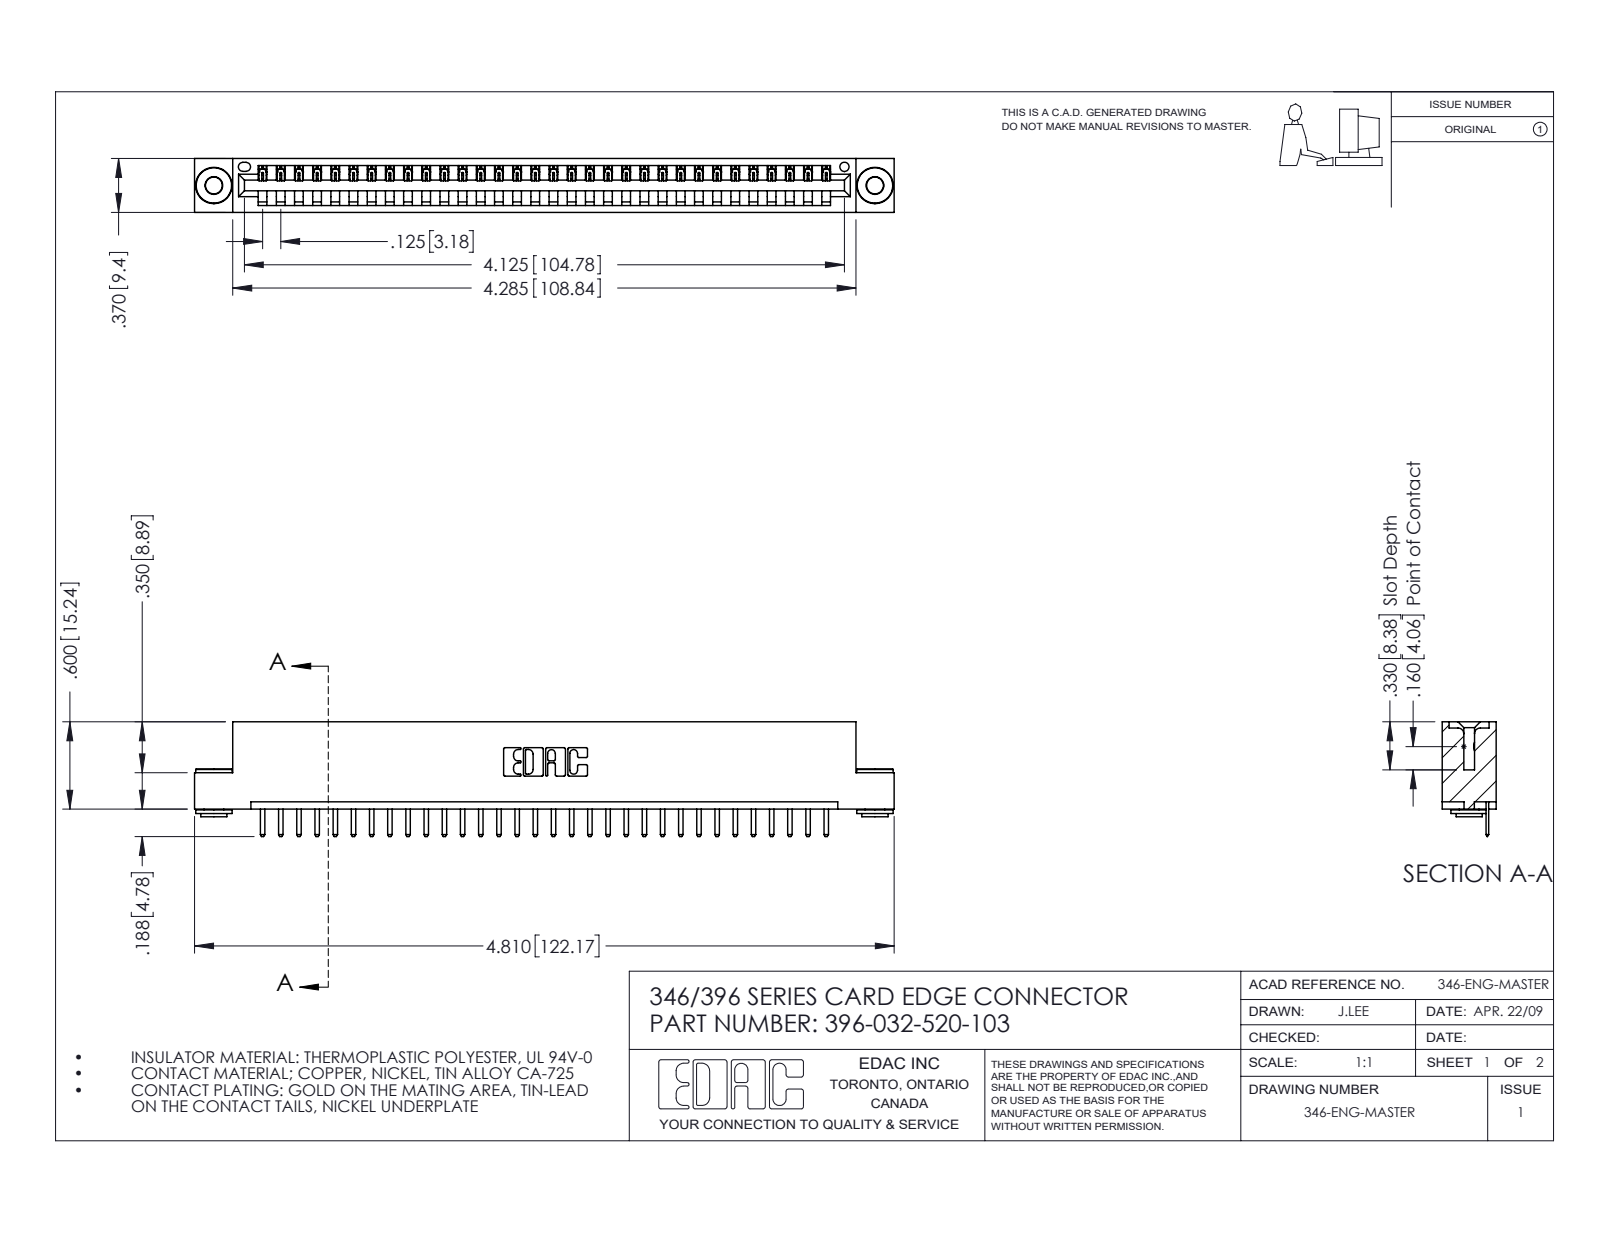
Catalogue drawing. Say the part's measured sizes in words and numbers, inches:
The part is named "345-250-002_345-250-002-102; 345-292-001_345-293-120; 396-032-520-103; 346 Part_Flush Mounting Lugs - 0.156 Dia-TH". Its 3-D file was written by "SolidWorks 2016 (CONFIG_CONTROL_DESIGN)". It is 35 solids with 2144 faces: 1430 planar, 706 cylindrical and 8 other. Overall it measures 4.81 by 0.788 by 0.37 inches. Its volume is 0.705 cubic inches and its surface area 22.08 square inches. Round holes: 2 of diameter 0.116, 2 of diameter 0.156, 1 of diameter 0.064. Round bosses or shafts: 2 of diameter 0.25, 2 of diameter 0.18, 2 of diameter 0.136. Partial cylindrical surfaces (rounded edges, fillets, slot ends): 66 of radius 0.01, 64 of radius 0.006, 22 of radius 0.01, 6 of radius 0.007, 6 of radius 0.031, 3 of radius 0.026, 2 of radius 0.031, 2 of radius 0.04. The main face-to-face distances are 0.048, 0.322, 0.37, 0.25, 0.148, 0.222, 0.1, 0.174, 0.025, 0.072. The hole center spacings are 0.246, 4.337, 4.545.
